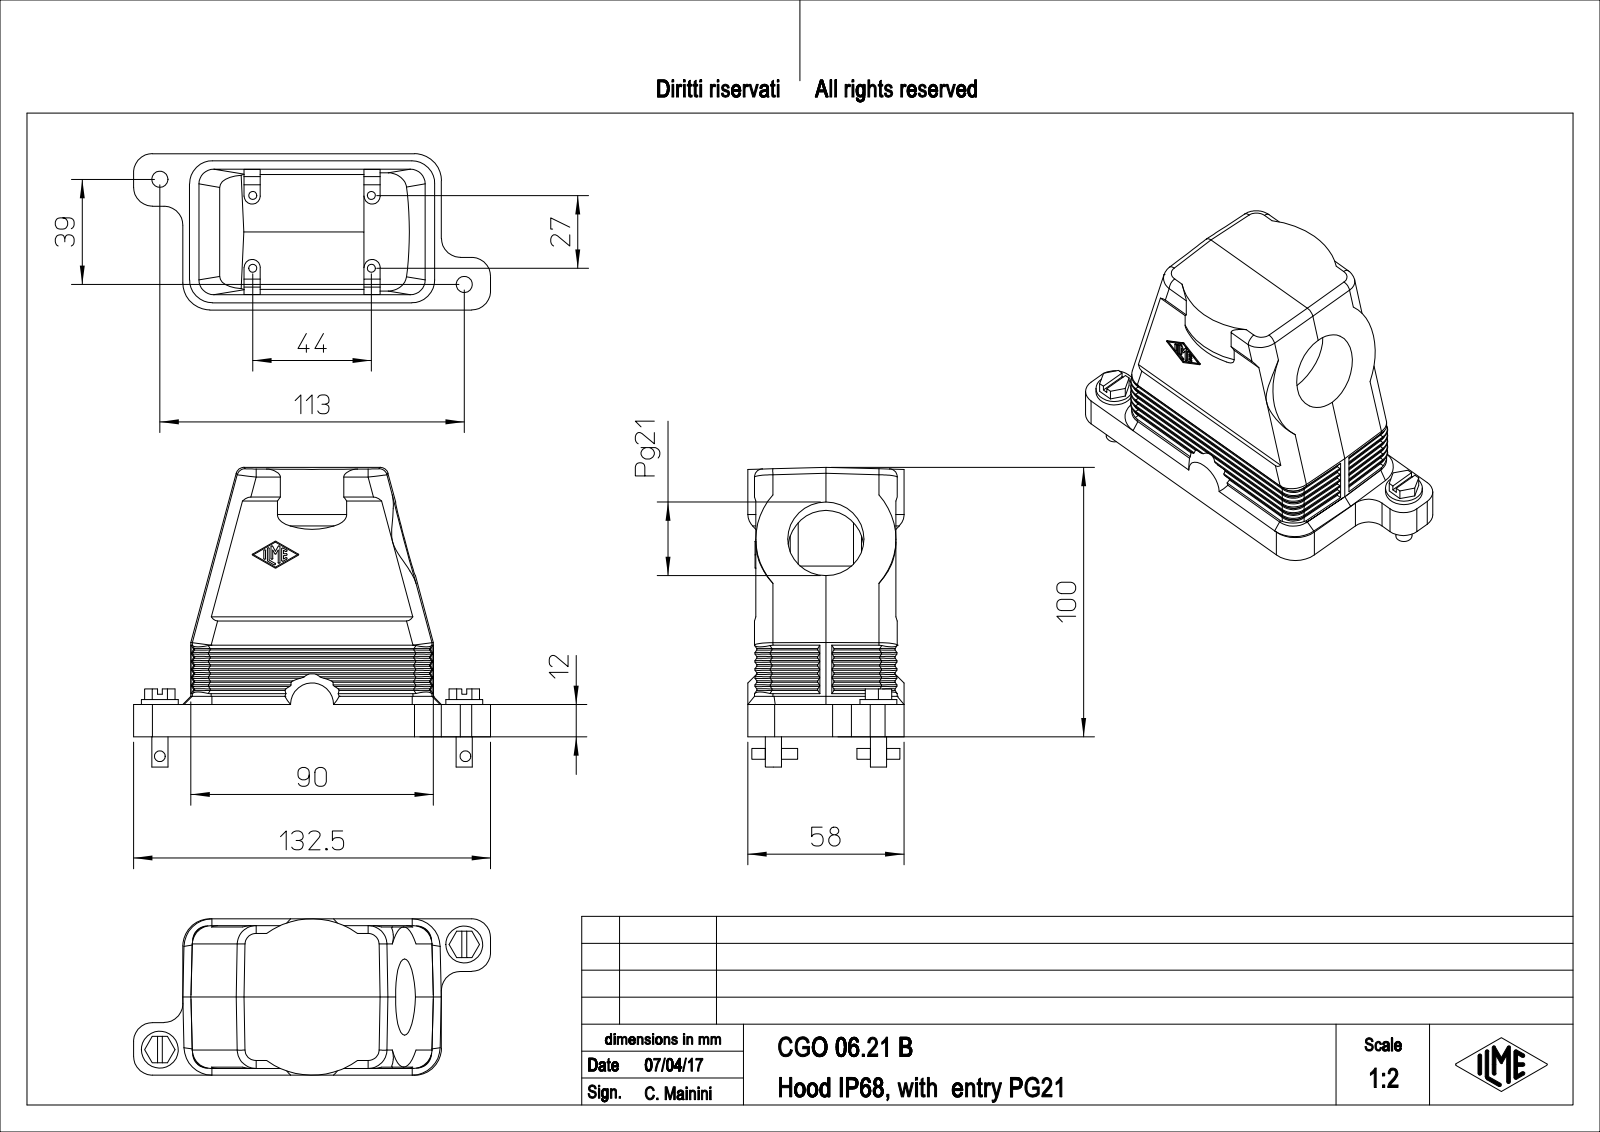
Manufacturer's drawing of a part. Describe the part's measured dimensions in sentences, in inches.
The part is named "CGO_06.21_B". Its 3-D file was written by "PTC Creo Elements/Direct Modeling 19.0E 27-Jun-2016 (C) Parametric Technology GmbH (AUTOMOTIVE_DESIGN)". It is 1 solid with 521 faces: 249 planar, 210 cylindrical and 62 other. Overall it measures 5.217 by 4.378 by 2.283 inches. Its volume is 8.817 cubic inches and its surface area 98.5 square inches. Round holes: 4 of diameter 0.118, 1 of diameter 1.114. Round bosses or shafts: 2 of diameter 0.539, 2 of diameter 0.236, 2 of diameter 0.079. Partial cylindrical surfaces (rounded edges, fillets, slot ends): 66 of radius 0.02, 62 of radius 0.276, 15 of radius 0.013, 6 of radius 0.118, 4 of radius 0.217, 4 of radius 0.335, 3 of radius 0.007, 2 of radius 0.394. The main face-to-face distances are 0.118, 2.165, 2.047, 0.098, 0.236, 1.752, 0.131, 0.02, 2.185, 2.067. The hole center spacings are 1.063, 1.732, 2.032.
